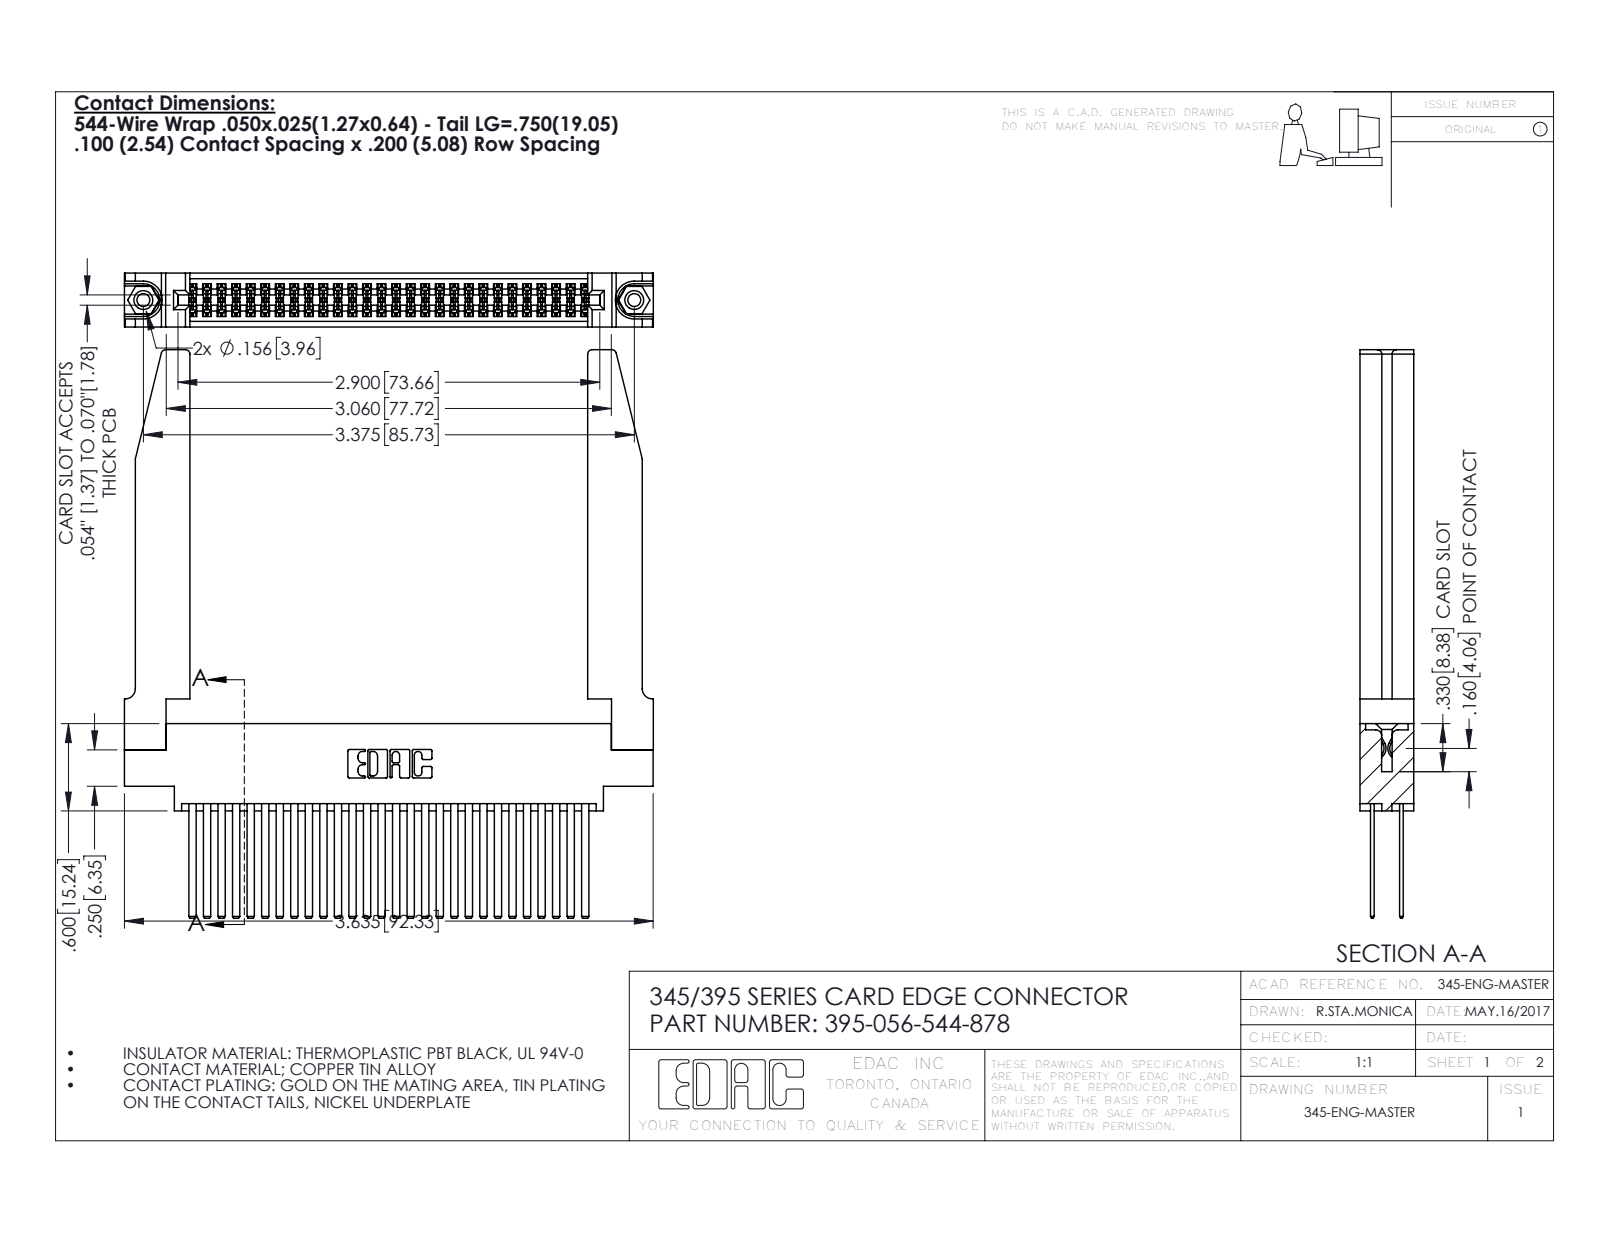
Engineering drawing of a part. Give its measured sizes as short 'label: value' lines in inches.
name: 345-220-078_345-220-078; 345 Part_0.170 Offset - 0.156 Dia-TH; 345-292-001_345-293-144; 395-056-544-878 (+1 more)
written by: SolidWorks 2016 (CONFIG_CONTROL_DESIGN)
unit: in
bodies: 61 solids, 2828 faces (1850 planar, 926 cylindrical, 52 other)
size: 3.907 × 3.636 × 0.37
volume: 1.055 in³; area: 35.76 in²
holes: 2× ⌀0.089, 2× ⌀0.125, 2× ⌀0.156, 1× ⌀0.064
bosses: 2× ⌀0.155
rounds: 84× R0.006, 22× R0.01, 8× R0.03, 6× R0.007, 6× R0.031, 3× R0.026, 2× R0.014, 2× R0.019
face distances: 0.072, 0.298, 0.37, 0.098, 0.272, 0.025, 0.2, 0.225, 0.175, 0.148
hole spacings: 0.27, 3.14, 3.375
